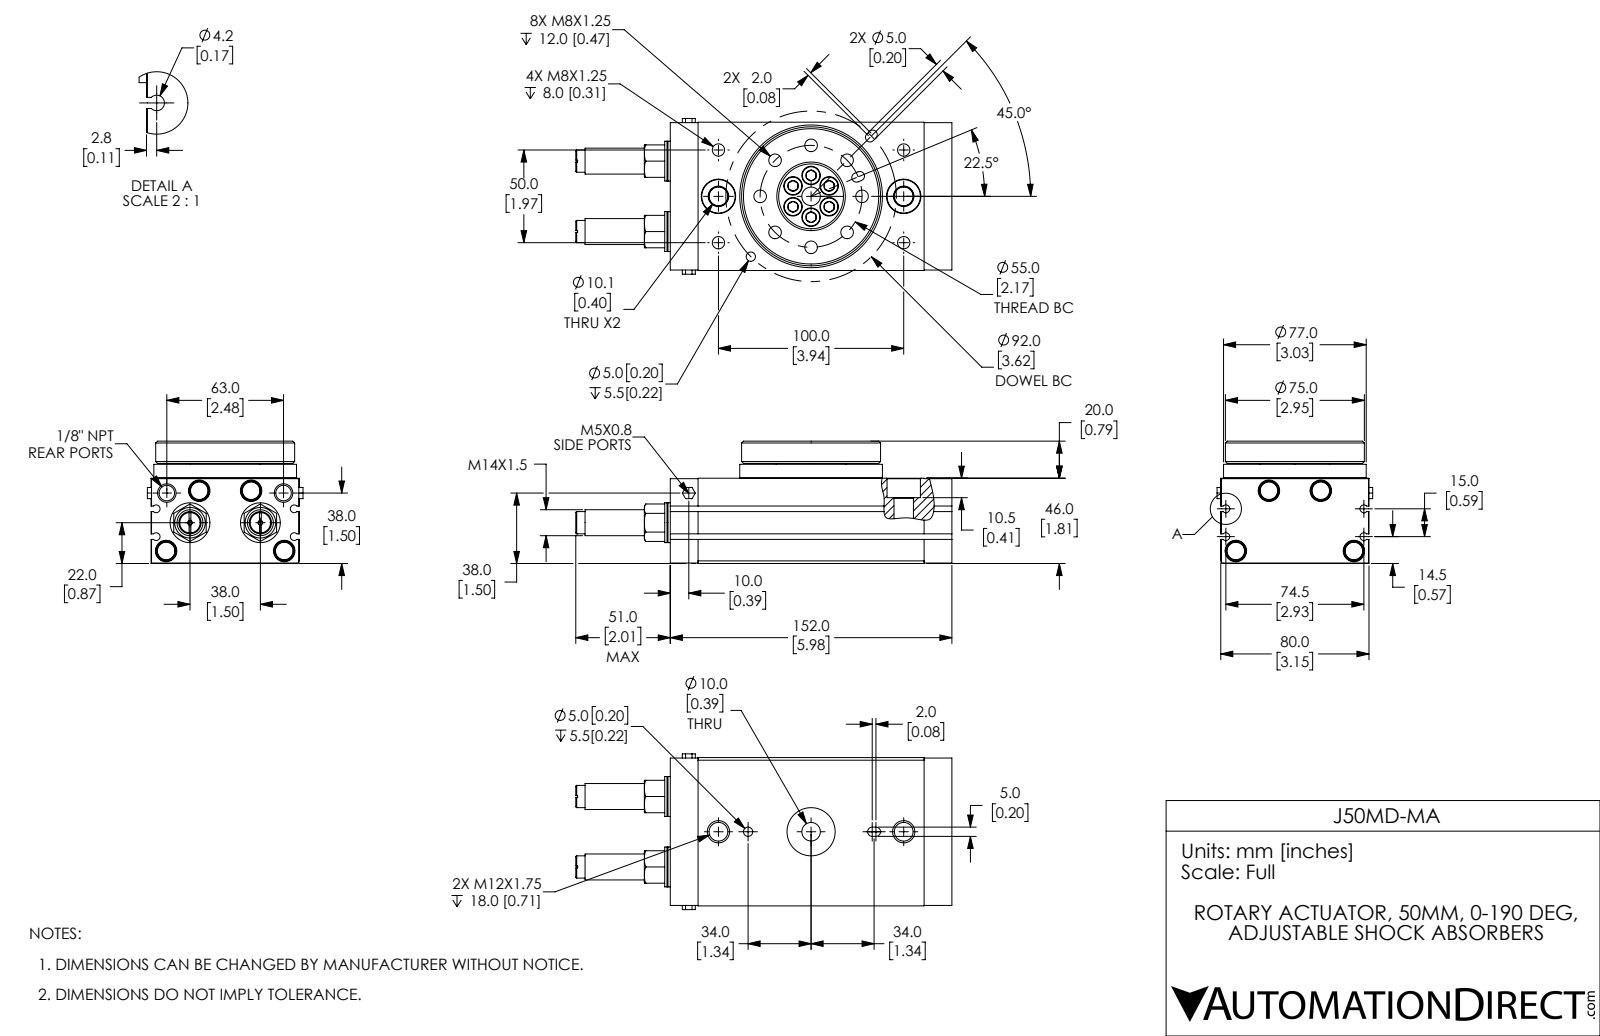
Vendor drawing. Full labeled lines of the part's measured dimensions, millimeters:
Part name (STEP PRODUCT): J50MD-MA_body2; J50MD-MA; J50MD-MA_M6_91290A310; J50MD-MA_table
STEP written by: SolidWorks 2017 (AUTOMOTIVE_DESIGN)
Units: millimetres
Bodies: 8 solids, 677 faces (197 planar, 290 cylindrical, 190 other)
Overall size (bounding box): 203 × 84 × 66
Volume: 619 979 mm³ · Surface area: 87 591 mm²
Round holes (diameter × count): ⌀6.8 ×8, ⌀6.65 ×4, ⌀11 ×4, ⌀6 ×3, ⌀2 ×2, ⌀8.38 ×2, ⌀10.11 ×2, ⌀10.5 ×2, ⌀18 ×2, ⌀10 ×1, ⌀26 ×1, ⌀35 ×1
Round bosses / shafts (diameter × count): ⌀10 ×10, ⌀6 ×6, ⌀4.7 ×6, ⌀21.5 ×2, ⌀14 ×2, ⌀12 ×2, ⌀77 ×1, ⌀75 ×1
Partial cylindrical surfaces — rounded edges, fillets, slot ends (radius × count): R2.5 ×6, R2.1 ×4
Main face-to-face distances: 46, 45.75, 80, 7.5, 12, 53.5, 8, 66, 12.5, 54
Hole centre spacings: 21.05, 50.82, 11.25, 25, 27.5, 27.51, 31.05, 33.63
